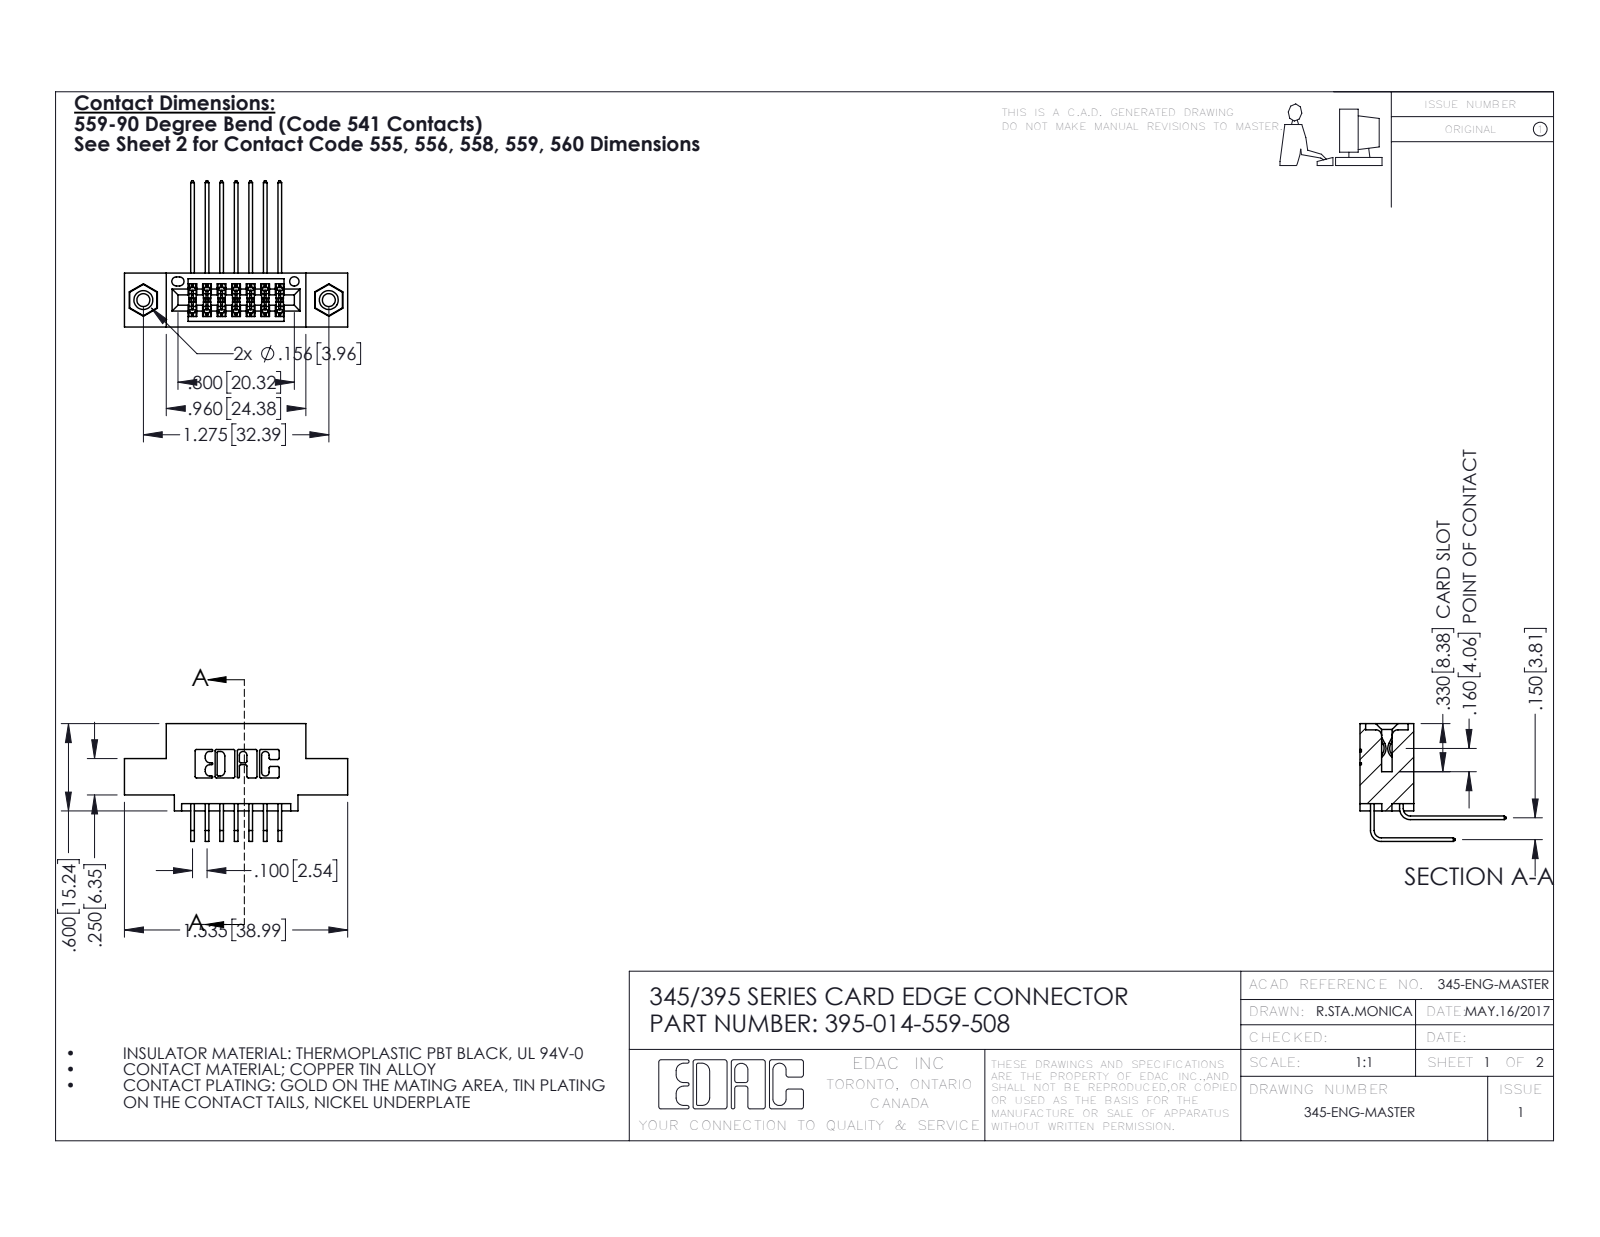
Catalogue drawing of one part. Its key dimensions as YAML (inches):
part_name: "345-292-001_559 Tail - 2; 395-014-559-508; 345-292-001_558 559 Tail - 1; 345-250-001_345-250-003-102 (+1 more)"
step_written_by: "SolidWorks 2016 (CONFIG_CONTROL_DESIGN)"
units: inches
bodies: {solids: 17, faces: 918, planar: 606, cylindrical: 296, other: 16}
overall_size: [1.535, 1.005, 0.809]
volume: 0.211
surface_area: 7.638
round_holes:
  - {diameter: 0.089, count: 2}
  - {diameter: 0.125, count: 2}
  - {diameter: 0.156, count: 2}
  - {diameter: 0.064, count: 1}
round_bosses_or_shafts:
  - {diameter: 0.155, count: 2}
partial_cylinders:
  - {radius: 0.006, count: 22}
  - {radius: 0.01, count: 22}
  - {radius: 0.007, count: 6}
  - {radius: 0.031, count: 6}
  - {radius: 0.026, count: 3}
  - {radius: 0.014, count: 2}
  - {radius: 0.019, count: 2}
  - {radius: 0.022, count: 2}
face_to_face_distances: [0.2, 0.072, 0.298, 0.37, 0.1, 0.098, 0.272, 0.025, 0.3, 0.15]
hole_center_spacings: [0.27, 1.045, 1.275]
